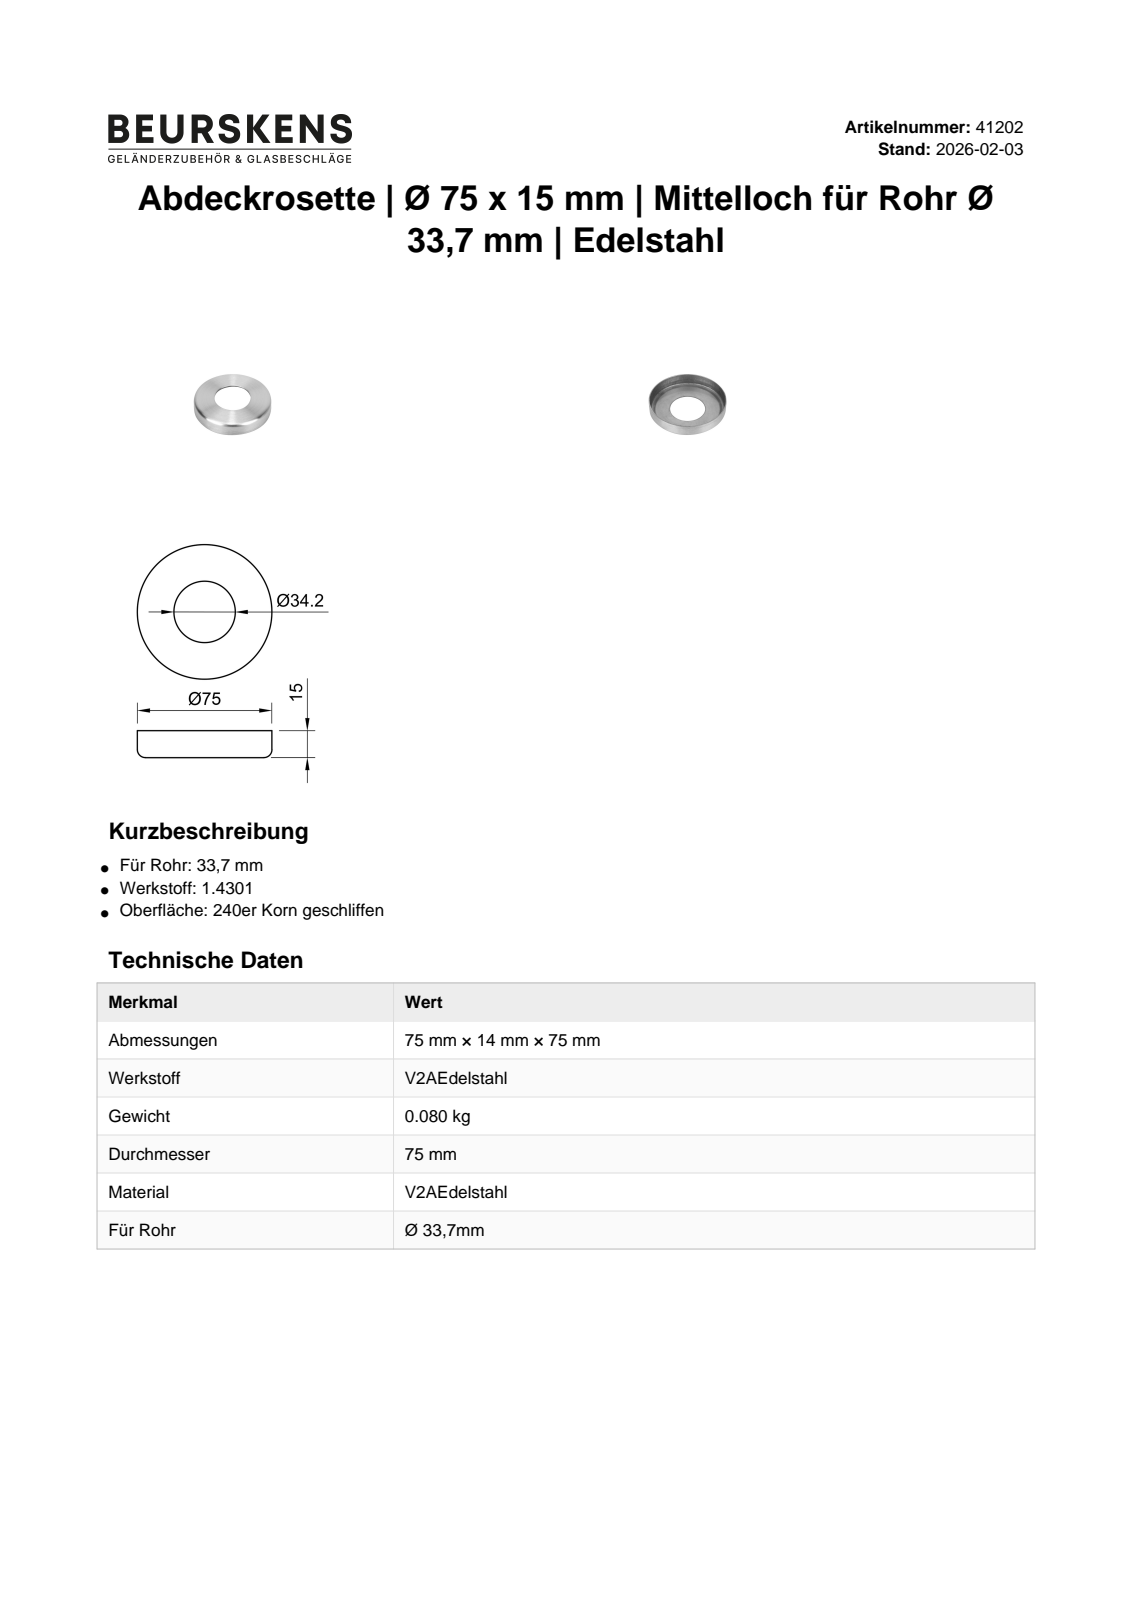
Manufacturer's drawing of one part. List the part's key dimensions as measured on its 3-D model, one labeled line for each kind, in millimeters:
Part name (STEP PRODUCT): 41202
STEP written by: Autodesk Inventor 2022 (AUTOMOTIVE_DESIGN)
Units: millimetres
Bodies: 1 solid, 8 faces (3 planar, 3 cylindrical, 2 other)
Overall size (bounding box): 75 × 75 × 15
Volume: 9 357 mm³ · Surface area: 12 988 mm²
Round holes (diameter × count): ⌀34.2 ×1, ⌀72 ×1
Round bosses / shafts (diameter × count): ⌀75 ×1
Main face-to-face distances: 1.5, 13.5, 15
